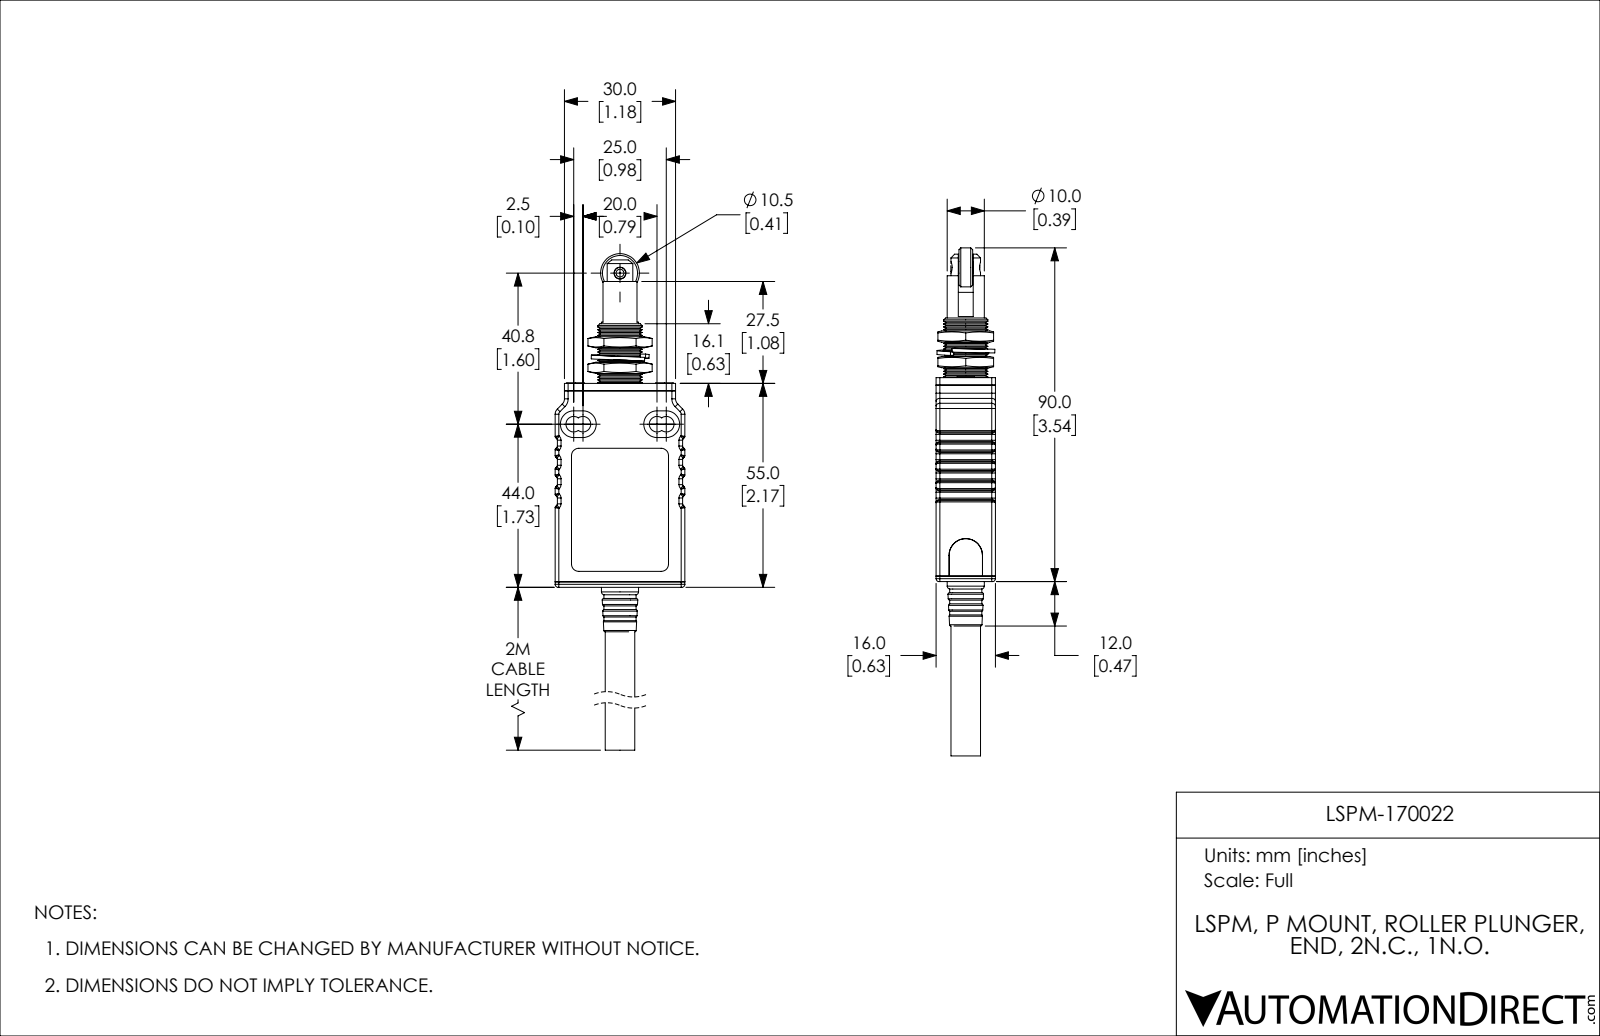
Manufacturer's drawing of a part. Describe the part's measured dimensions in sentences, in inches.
The part is named "170-LSPM-Panel Mount Roller Plunger-Bottom Cable (STEP format)". Its 3-D file was written by "SolidWorks 2013 (CONFIG_CONTROL_DESIGN)". It is 15 solids with 838 faces: 268 planar, 313 cylindrical and 257 other. Overall it measures 5.394 by 1.378 by 0.63 inches. Its volume is 1.192 cubic inches and its surface area 33.84 square inches. Round holes: 2 of diameter 0.079, 2 of diameter 0.098, 2 of diameter 0.102, 1 of diameter 0.059, 1 of diameter 0.094, 1 of diameter 0.114, 1 of diameter 0.126, 1 of diameter 0.157, 1 of diameter 0.213, 1 of diameter 0.323, 1 of diameter 0.354, 1 of diameter 0.441. Round bosses or shafts: 2 of diameter 0.185, 1 of diameter 0.579, 1 of diameter 0.469, 1 of diameter 0.433, 1 of diameter 0.417, 1 of diameter 0.413, 1 of diameter 0.394, 1 of diameter 0.386. Partial cylindrical surfaces (rounded edges, fillets, slot ends): 74 of radius 0.02, 52 of radius 0.039, 8 of radius 0.079, 4 of radius 0.031, 4 of radius 0.083, 4 of radius 0.142, 3 of radius 0.012, 2 of radius 0.008. The main face-to-face distances are 0.059, 0.618, 0.039, 0.571, 0.047, 0.559, 0.079, 0.098, 0.512, 0.606. The hole center spacings are 0.472, 0.945.
